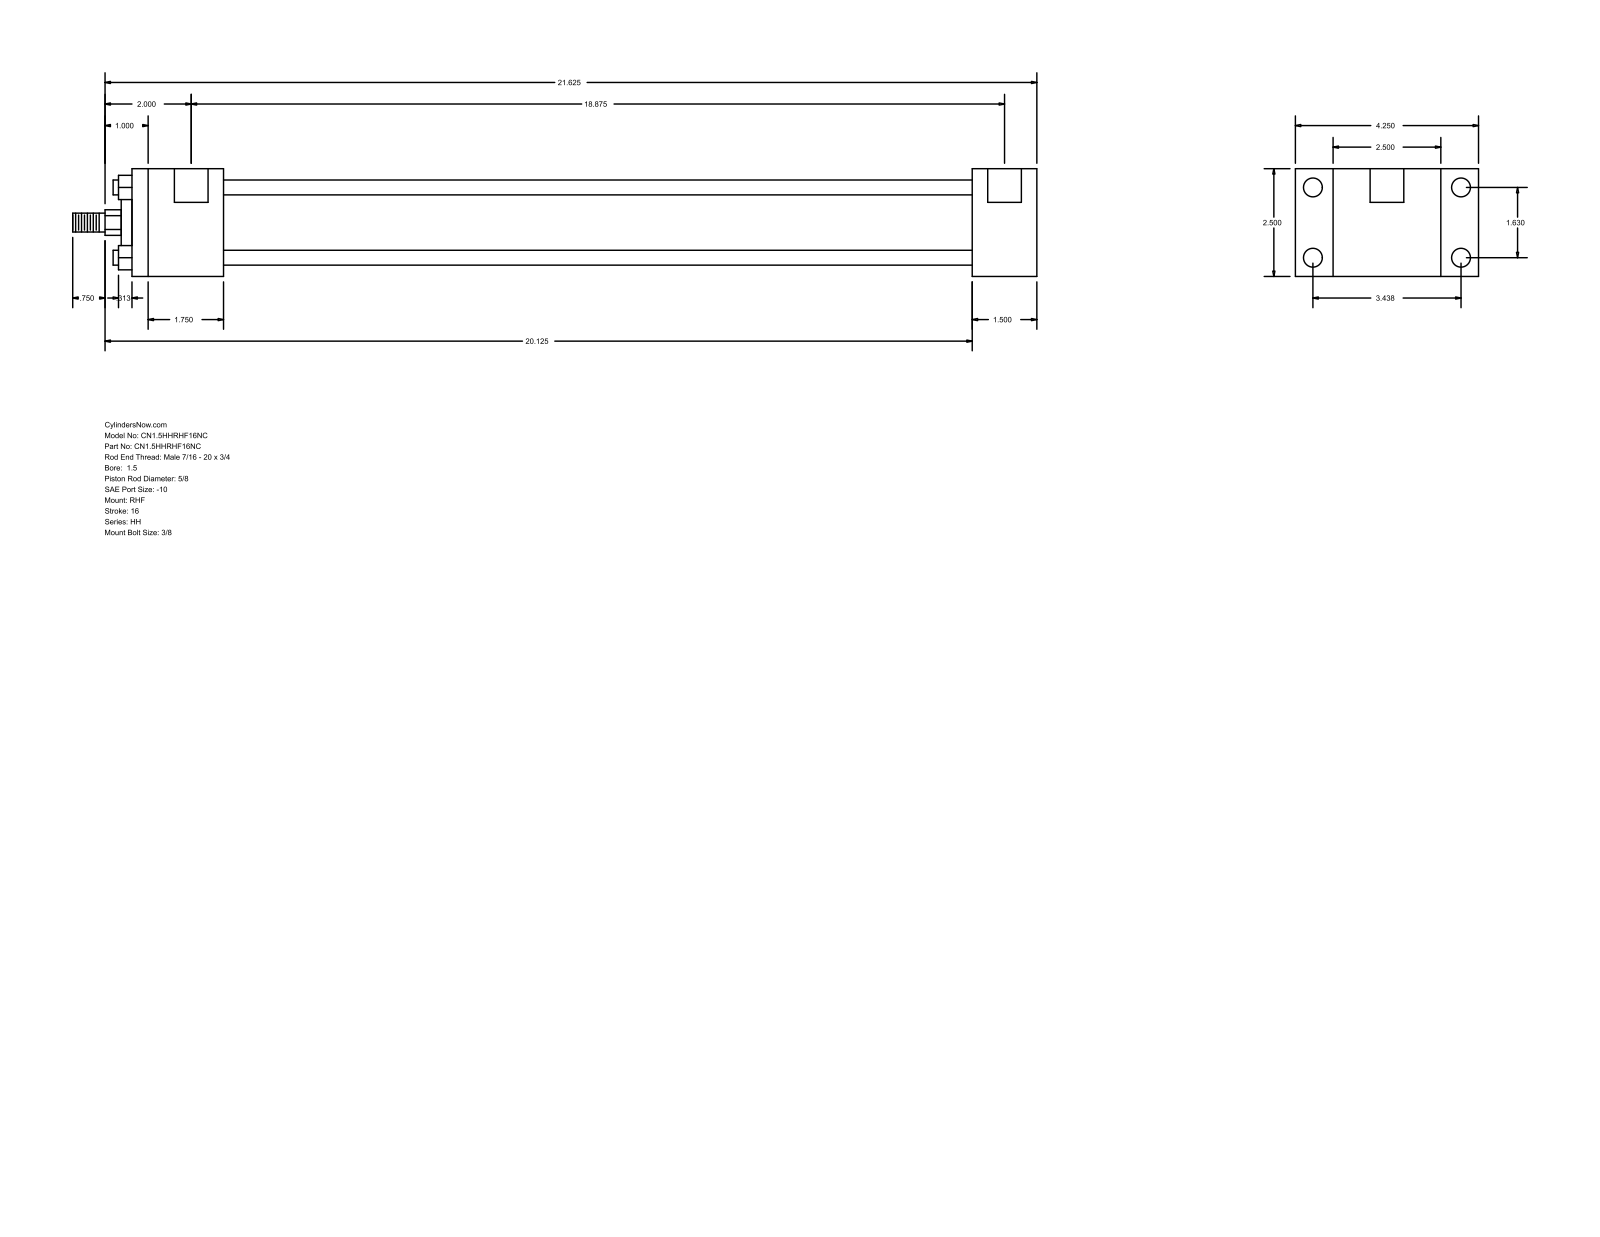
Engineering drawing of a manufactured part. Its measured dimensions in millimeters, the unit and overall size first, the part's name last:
Units: millimetres
Overall size (bounding box): 568.33 × 107.95 × 63.5
Round holes (diameter × count): ⌀5.56 ×4, ⌀11.13 ×4, ⌀19.84 ×2
Round bosses / shafts (diameter × count): ⌀8.76 ×4, ⌀44.45 ×1, ⌀28.57 ×1, ⌀15.88 ×1, ⌀11.11 ×1
Partial cylindrical surfaces — rounded edges, fillets, slot ends (radius × count): R7.54 ×1
Main face-to-face distances: 63.5, 22.23, 85.73, 38.09, 495.3, 533.39, 107.96, 53.97, 441.33, 479.42
Hole centre spacings: 41.4, 87.32, 96.64, 482.6, 1.58, 1.59, 479.43, 481.01
Bodies: 0 solids, 88 faces (60 planar, 28 cylindrical, 0 other)
Part name (STEP PRODUCT): HH_RHF__0150_0.625
STEP written by: GSSL Pune (CONFIG_CONTROL_DESIGN)
